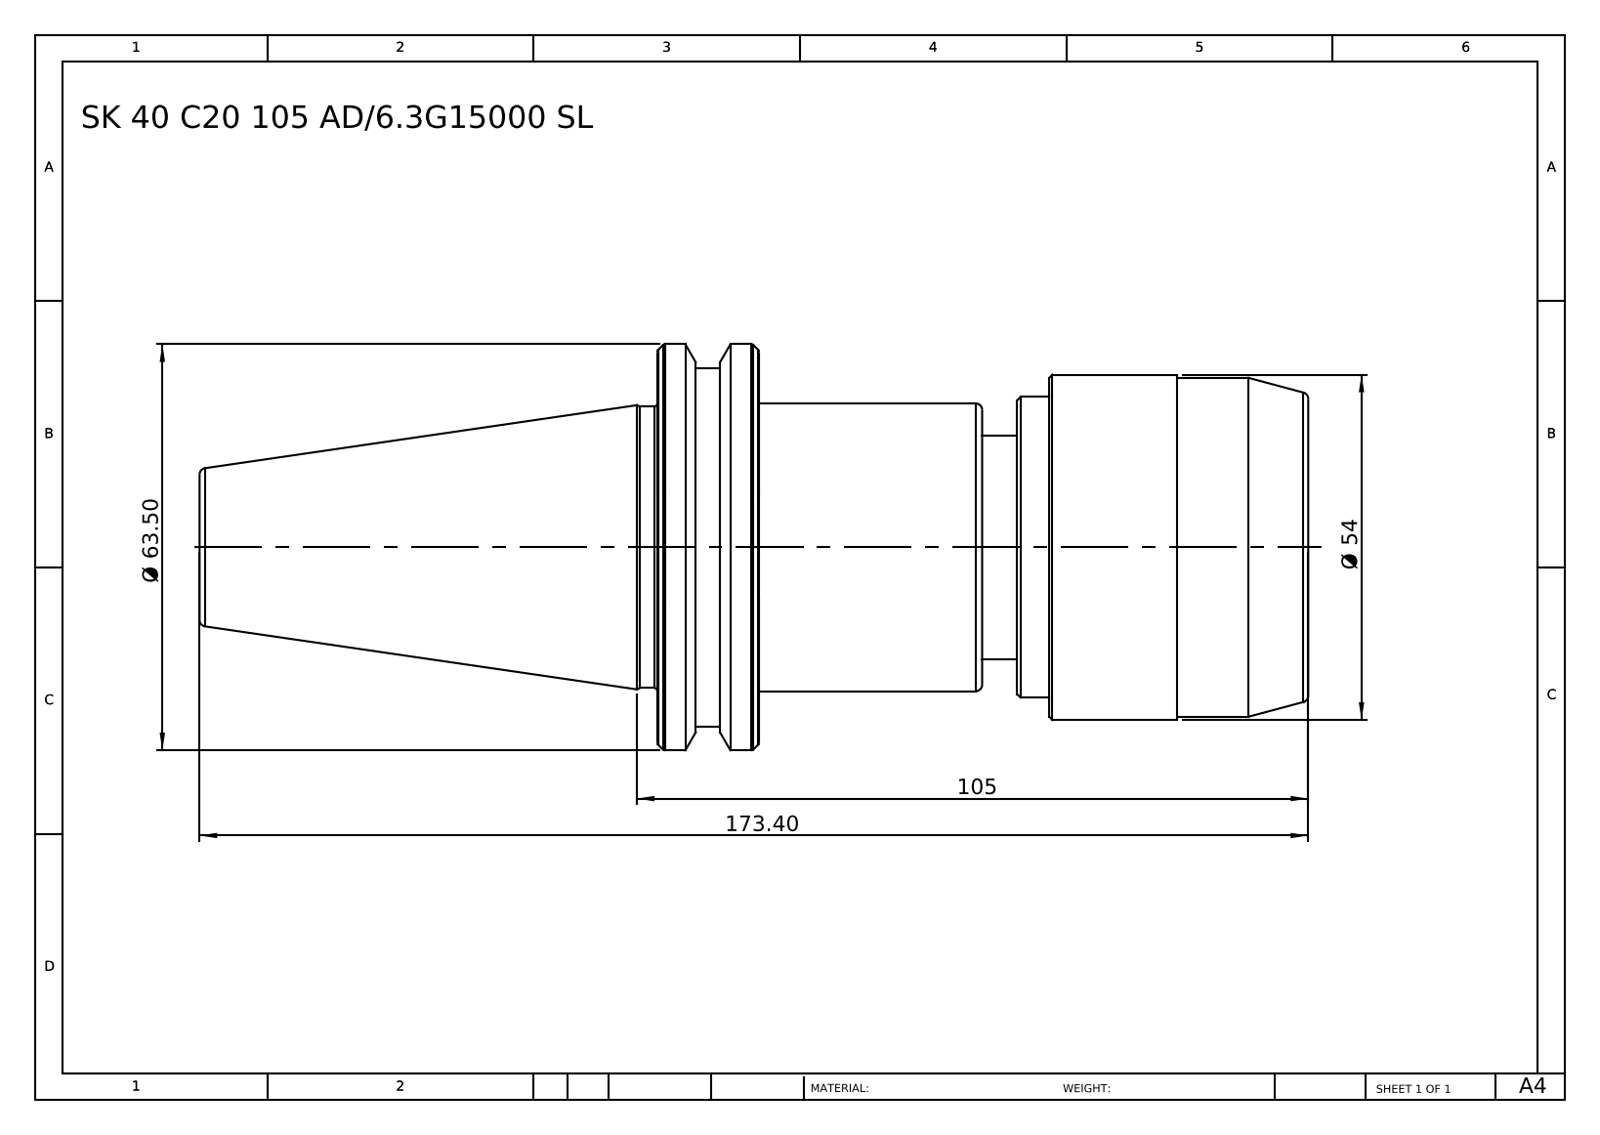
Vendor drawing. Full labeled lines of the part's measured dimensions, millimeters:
Part name (STEP PRODUCT): SK 40 C20 105 AD-6.3G15000 SL
STEP written by: SolidWorks 2014 (CONFIG_CONTROL_DESIGN)
Units: millimetres
Bodies: 1 solid, 82 faces (10 planar, 18 cylindrical, 54 other)
Overall size (bounding box): 173.4 × 63.5 × 63.5
Volume: 275 651 mm³ · Surface area: 32 060 mm²
Round bosses / shafts (diameter × count): ⌀63.5 ×1, ⌀56 ×1, ⌀54 ×1, ⌀53 ×1, ⌀47 ×1, ⌀45 ×1, ⌀44 ×1, ⌀35 ×1
Main face-to-face distances: 101.8, 85.9, 15.9, 45.5, 40.4, 56.3, 51, 5.5, 34.9, 50.8
